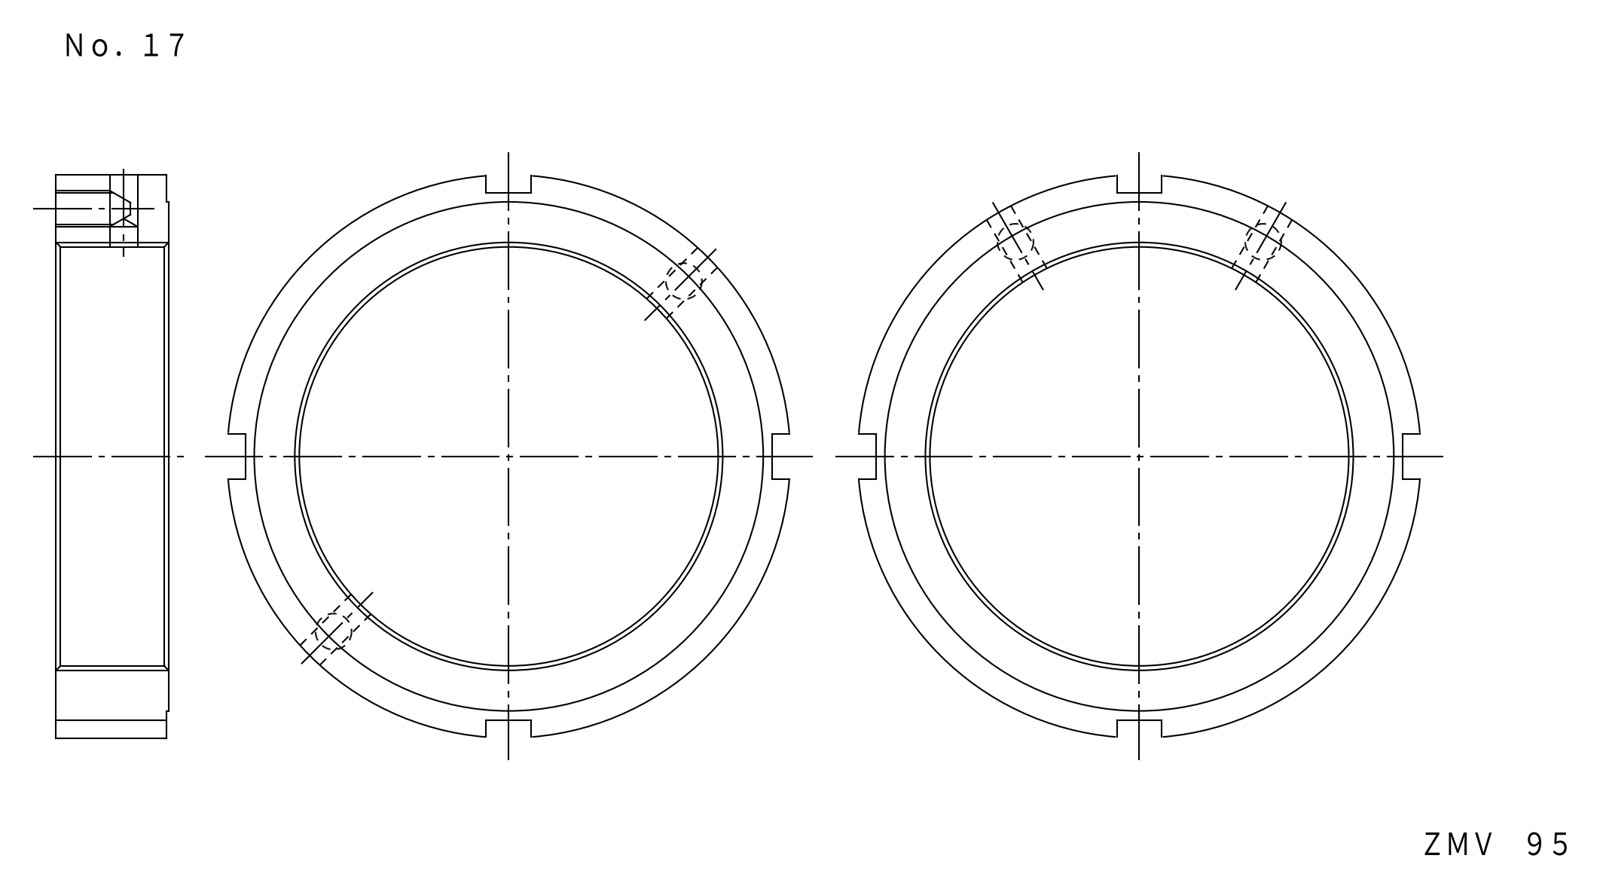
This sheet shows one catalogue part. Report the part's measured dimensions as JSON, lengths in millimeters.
{"part_name": "FKD ZMV95", "step_written_by": "Autodesk Inventor LT (CONFIG_CONTROL_DESIGN)", "units": "millimeters", "bodies": {"solids": 1, "faces": 29, "planar": 15, "cylindrical": 10, "other": 4}, "overall_size": [124.6, 124.6, 25], "volume_mm3": 122843, "surface_area_mm2": 28914, "round_holes": [[6.2, 2], [6.65, 2], [95, 1]], "round_bosses_or_shafts": [[125, 1], [113, 1]], "face_to_face_distances": [25, 0.5, 24.5, 53.5, 63.5, 117, 10], "hole_center_spacings": [55, 110]}
